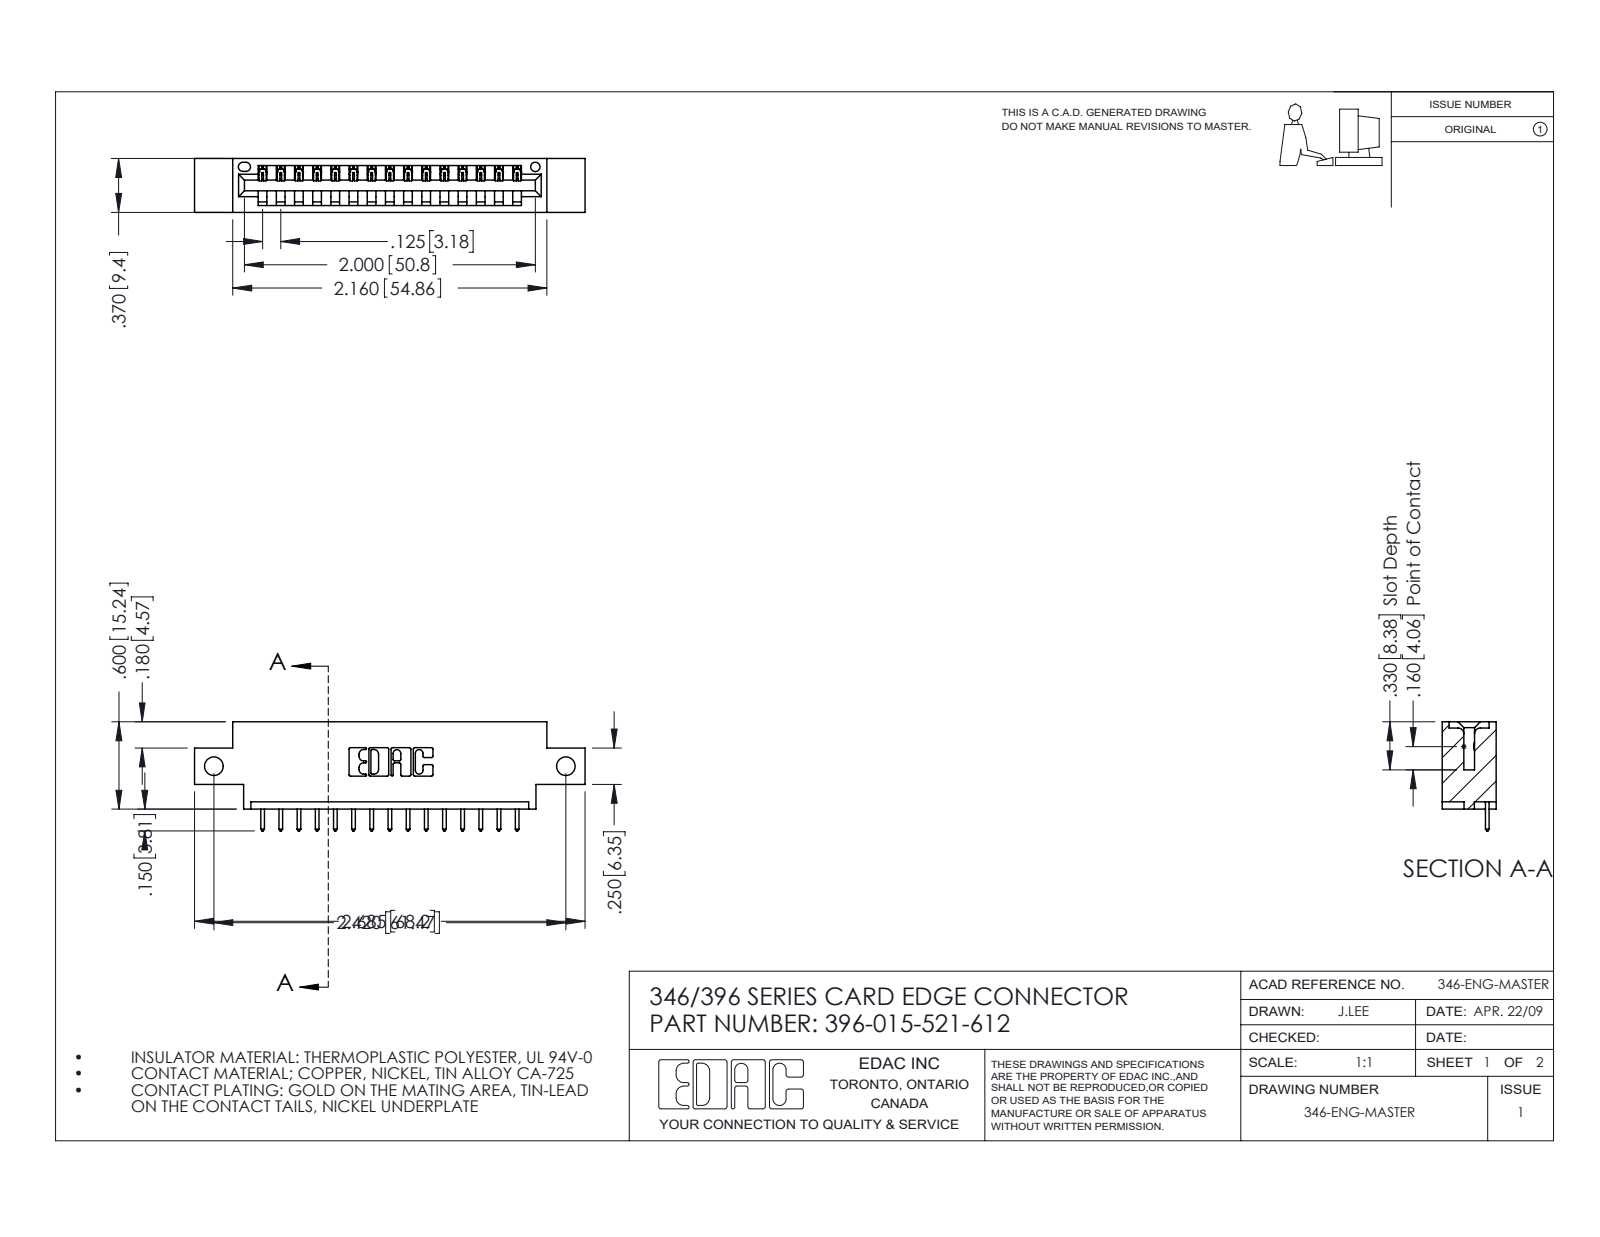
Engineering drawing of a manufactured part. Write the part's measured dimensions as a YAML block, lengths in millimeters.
part_name: "396-015-521-612; 346 Part_0.170 Offset - Side Mount; 345-292-001_345-293-121"
step_written_by: "SolidWorks 2016 (CONFIG_CONTROL_DESIGN)"
units: millimeters
bodies: {solids: 16, faces: 996, planar: 680, cylindrical: 316, other: 0}
overall_size: [68.2, 19.1, 9.4]
volume: 6060
surface_area: 7123
round_holes:
  - {diameter: 3.3, count: 2}
  - {diameter: 1.6, count: 1}
partial_cylinders:
  - {radius: 0.2, count: 30}
  - {radius: 0.3, count: 30}
  - {radius: 0.3, count: 22}
  - {radius: 0.2, count: 6}
  - {radius: 0.8, count: 6}
  - {radius: 0.7, count: 3}
  - {radius: 0.8, count: 2}
  - {radius: 1, count: 2}
face_to_face_distances: [9.4, 1.2, 8.2, 6.4, 1.8, 7.6, 0.6, 3.8, 5.6, 2.5]
hole_center_spacings: [61.5]
